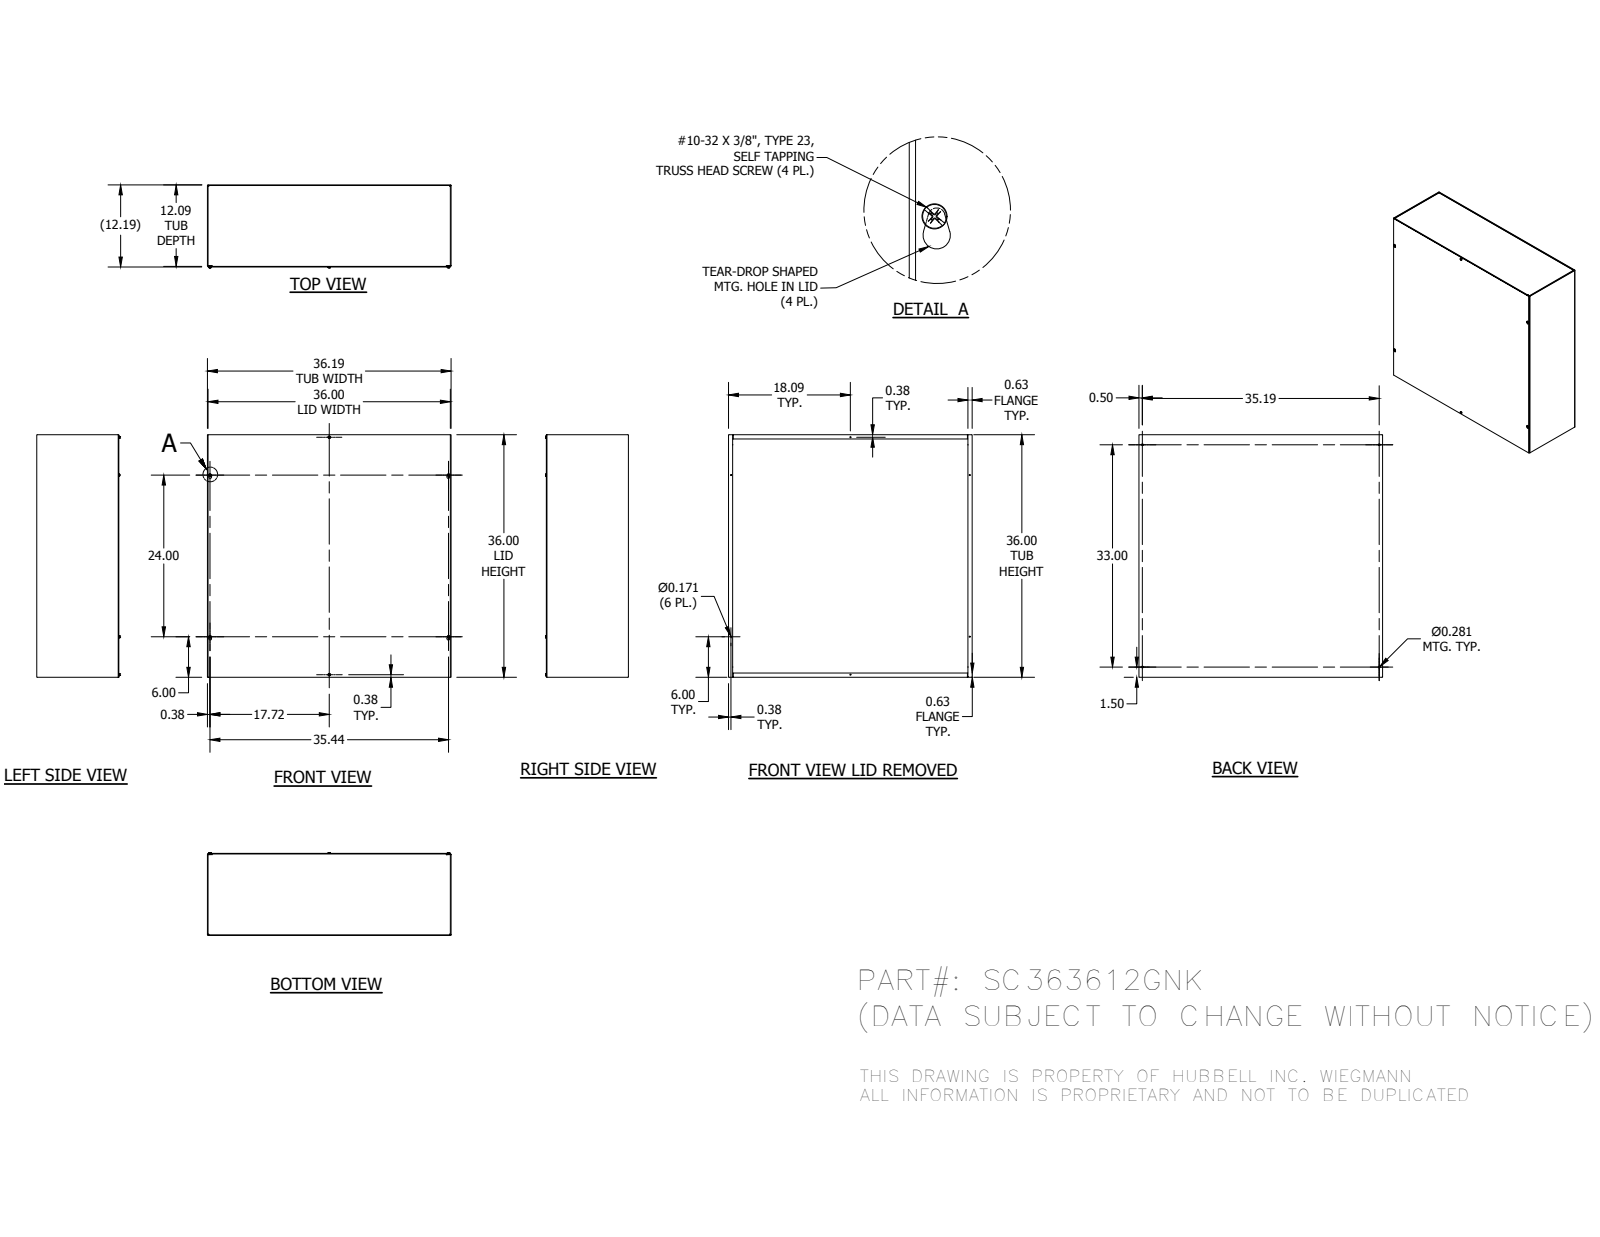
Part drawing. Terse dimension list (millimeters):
name: SC363612GNKBLR; SC3612GNKTB; SC3636GLPA; 37214 (+1 more)
written by: Autodesk Inventor 2014 (AUTOMOTIVE_DESIGN)
unit: mm
bodies: 10 solids, 404 faces (232 planar, 50 cylindrical, 122 other)
size: 919.16 × 914.4 × 312.91
volume: 6 845 000 mm³; area: 5 784 000 mm²
holes: 6× ⌀4.34, 4× ⌀7.14, 2× ⌀7.92
bosses: 6× ⌀4.83
rounds: 12× R0.4, 12× R2.78, 4× R3.17, 4× R5.16
face distances: 2.38, 307.18, 304.8, 309.56, 914.4, 912.02, 916.78, 909.64, 919.16, 4.76
hole spacings: 447.79, 114.34, 472.19, 723.91, 876.79, 904.19, 975.19, 1152.62
